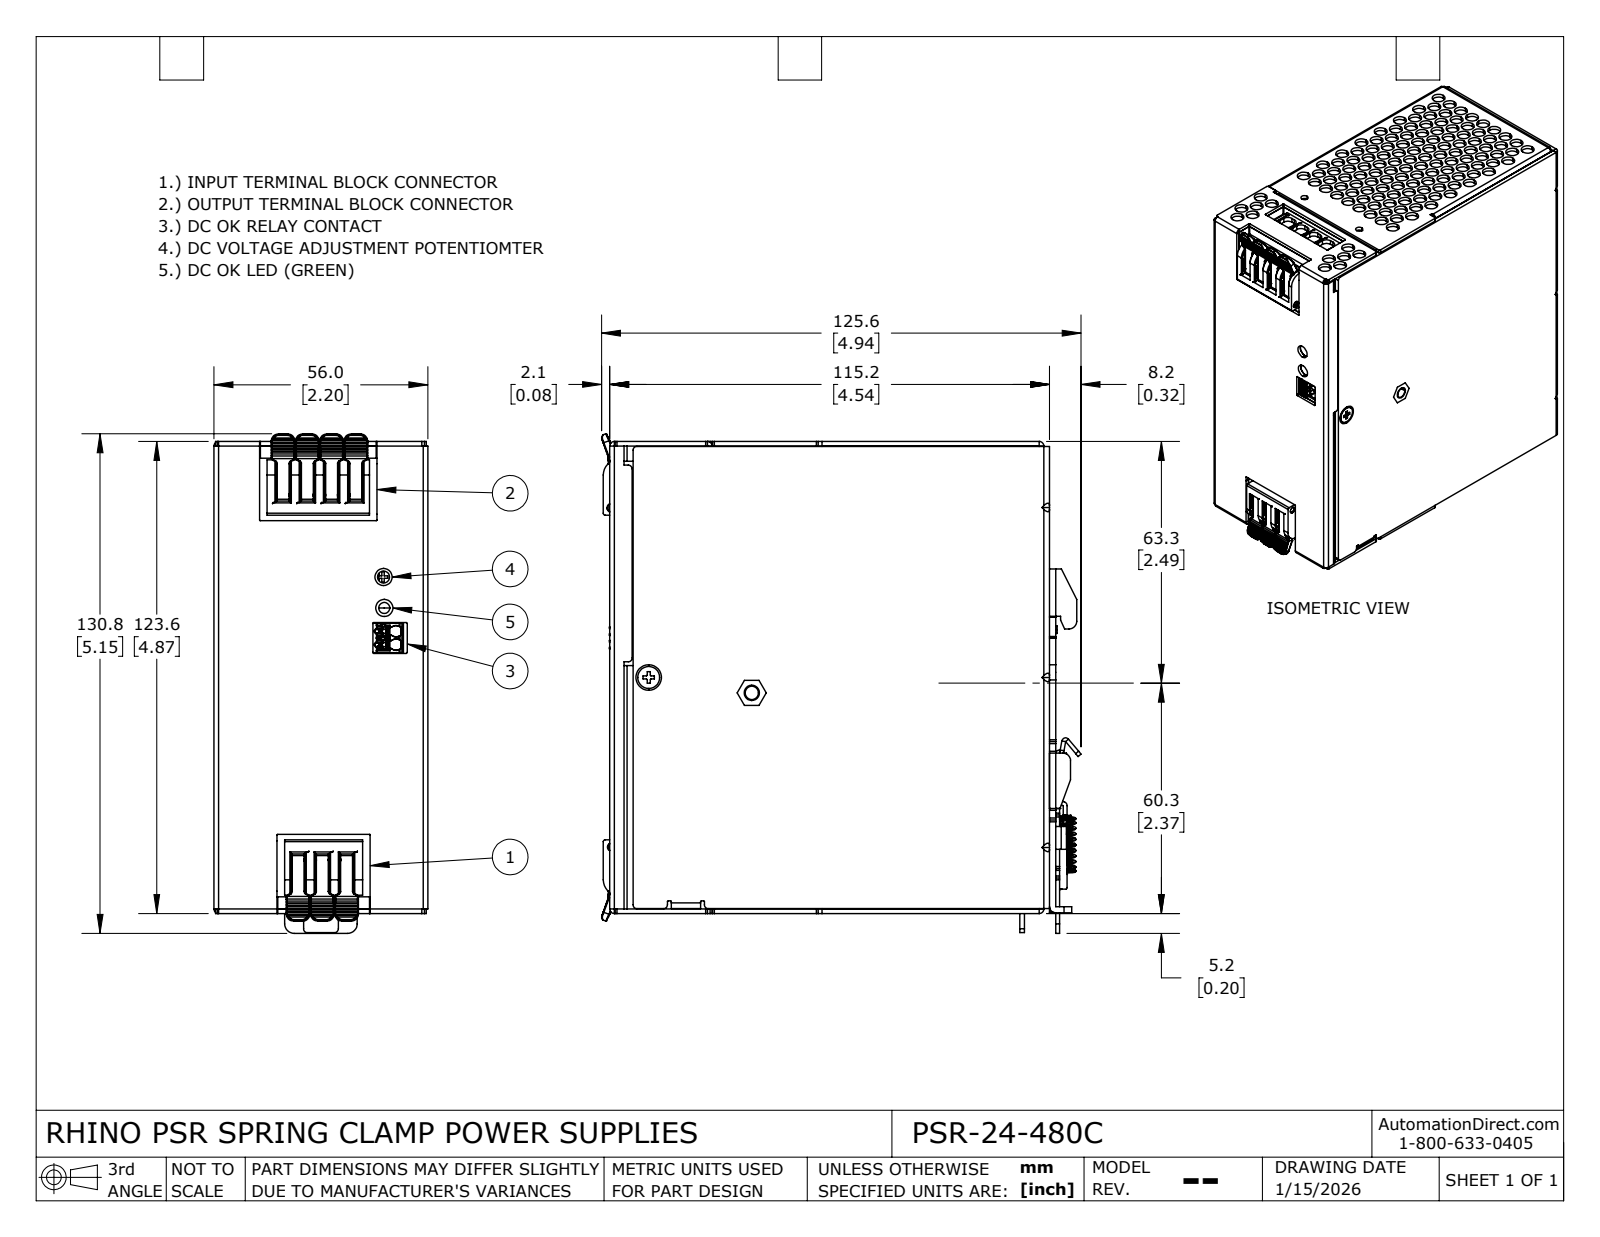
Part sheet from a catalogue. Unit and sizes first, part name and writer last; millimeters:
Units: millimetres
Overall size (bounding box): 130.8 × 125.6 × 56
Round holes (diameter × count): ⌀4.5 ×142, ⌀3.7 ×5, ⌀3.5 ×4, ⌀6.7 ×3, ⌀1 ×2, ⌀2.2 ×2, ⌀2.3 ×2, ⌀2.5 ×2, ⌀3 ×2, ⌀3.2 ×2, ⌀3.6 ×2
Round bosses / shafts (diameter × count): ⌀5.7 ×5, ⌀3 ×3, ⌀6.4 ×2, ⌀5.4 ×2, ⌀2.4 ×2, ⌀2.1 ×2, ⌀2 ×2, ⌀6.5 ×1
Partial cylindrical surfaces — rounded edges, fillets, slot ends (radius × count): R0.2 ×265, R0.5 ×123, R0.3 ×66, R2 ×54, R0.4 ×28, R1 ×27, R0.3 ×20, R1.2 ×20
Main face-to-face distances: 1.2, 54.8, 56, 112.5, 121.2, 1.6, 122.4, 1.5, 114, 115.6
Hole centre spacings: 5.5, 5.5, 9.5, 11, 11, 14.6, 14.5, 14.5
Volume: 796 700 mm³ · Surface area: 141 900 mm²
Bodies: 7 solids, 4472 faces (1730 planar, 2039 cylindrical, 703 other)
Part name (STEP PRODUCT): PSR-24-480C
STEP written by: SolidWorks 2024 (AUTOMOTIVE_DESIGN)
